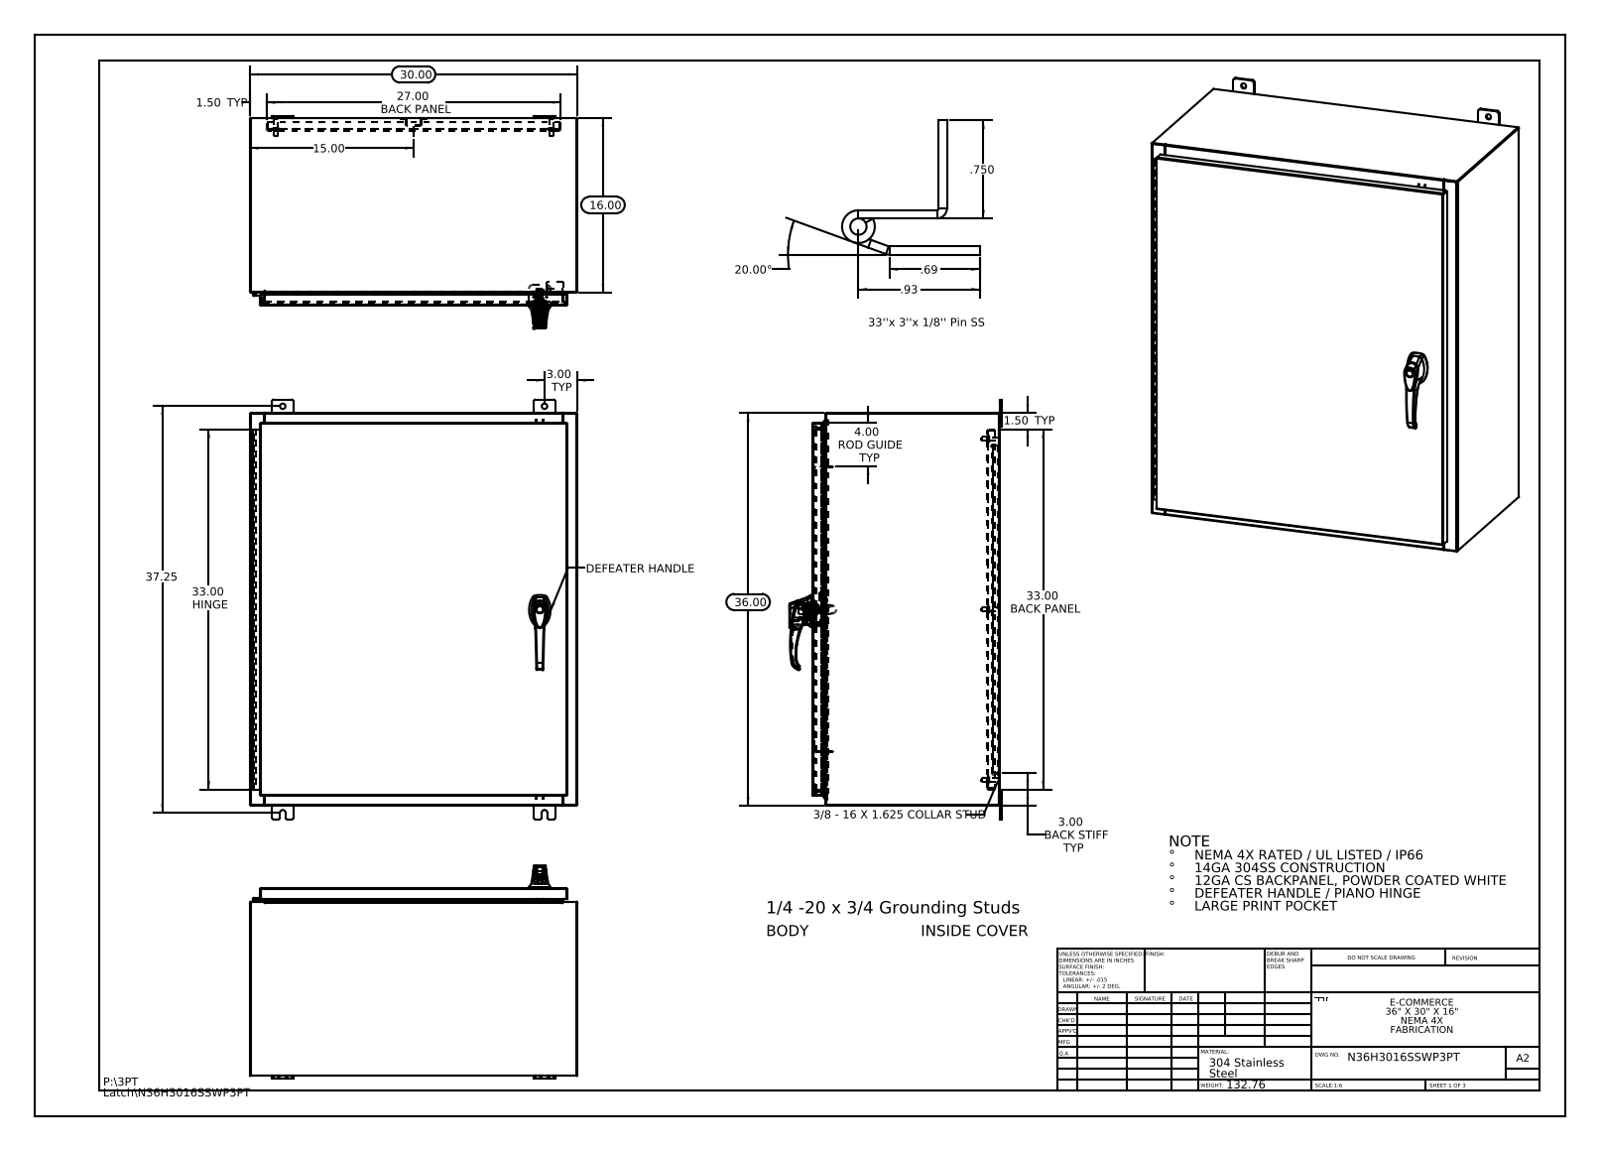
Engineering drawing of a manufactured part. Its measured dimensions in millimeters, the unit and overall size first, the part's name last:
Units: millimetres
Overall size (bounding box): 977.9 × 762 × 495.2
Round holes (diameter × count): ⌀12.7 ×10, ⌀6.4 ×4, ⌀3.5 ×3, ⌀4.1 ×3, ⌀2 ×2, ⌀5.2 ×2, ⌀8 ×2, ⌀11.1 ×2, ⌀3.2 ×1, ⌀3.2 ×1, ⌀5 ×1, ⌀7 ×1
Round bosses / shafts (diameter × count): ⌀15.9 ×6, ⌀9.5 ×6, ⌀8.4 ×6, ⌀30 ×1, ⌀19 ×1, ⌀17.3 ×1, ⌀16.8 ×1, ⌀16.2 ×1
Partial cylindrical surfaces — rounded edges, fillets, slot ends (radius × count): R3 ×37, R0.2 ×33, R0.3 ×28, R4.8 ×24, R2.2 ×22, R1 ×15, R0.7 ×12, R0.2 ×6
Main face-to-face distances: 1.9, 435, 760.1, 433.1, 2.6, 436.9, 912.5, 25.4, 409.6, 27.3
Hole centre spacings: 288.6, 347.2, 396.9, 754.2, 641.4, 714.5, 7.5, 15.9
Volume: 7 666 000 mm³ · Surface area: 7 554 000 mm²
Bodies: 34 solids, 2808 faces (1065 planar, 1069 cylindrical, 674 other)
Part name (STEP PRODUCT): 21130102; N36H3016SSWP3PT Enclosure Stiffener; 022151; N36H3016SSWP3PT Body (+8 more)
STEP written by: SolidWorks 2013 (CONFIG_CONTROL_DESIGN)
